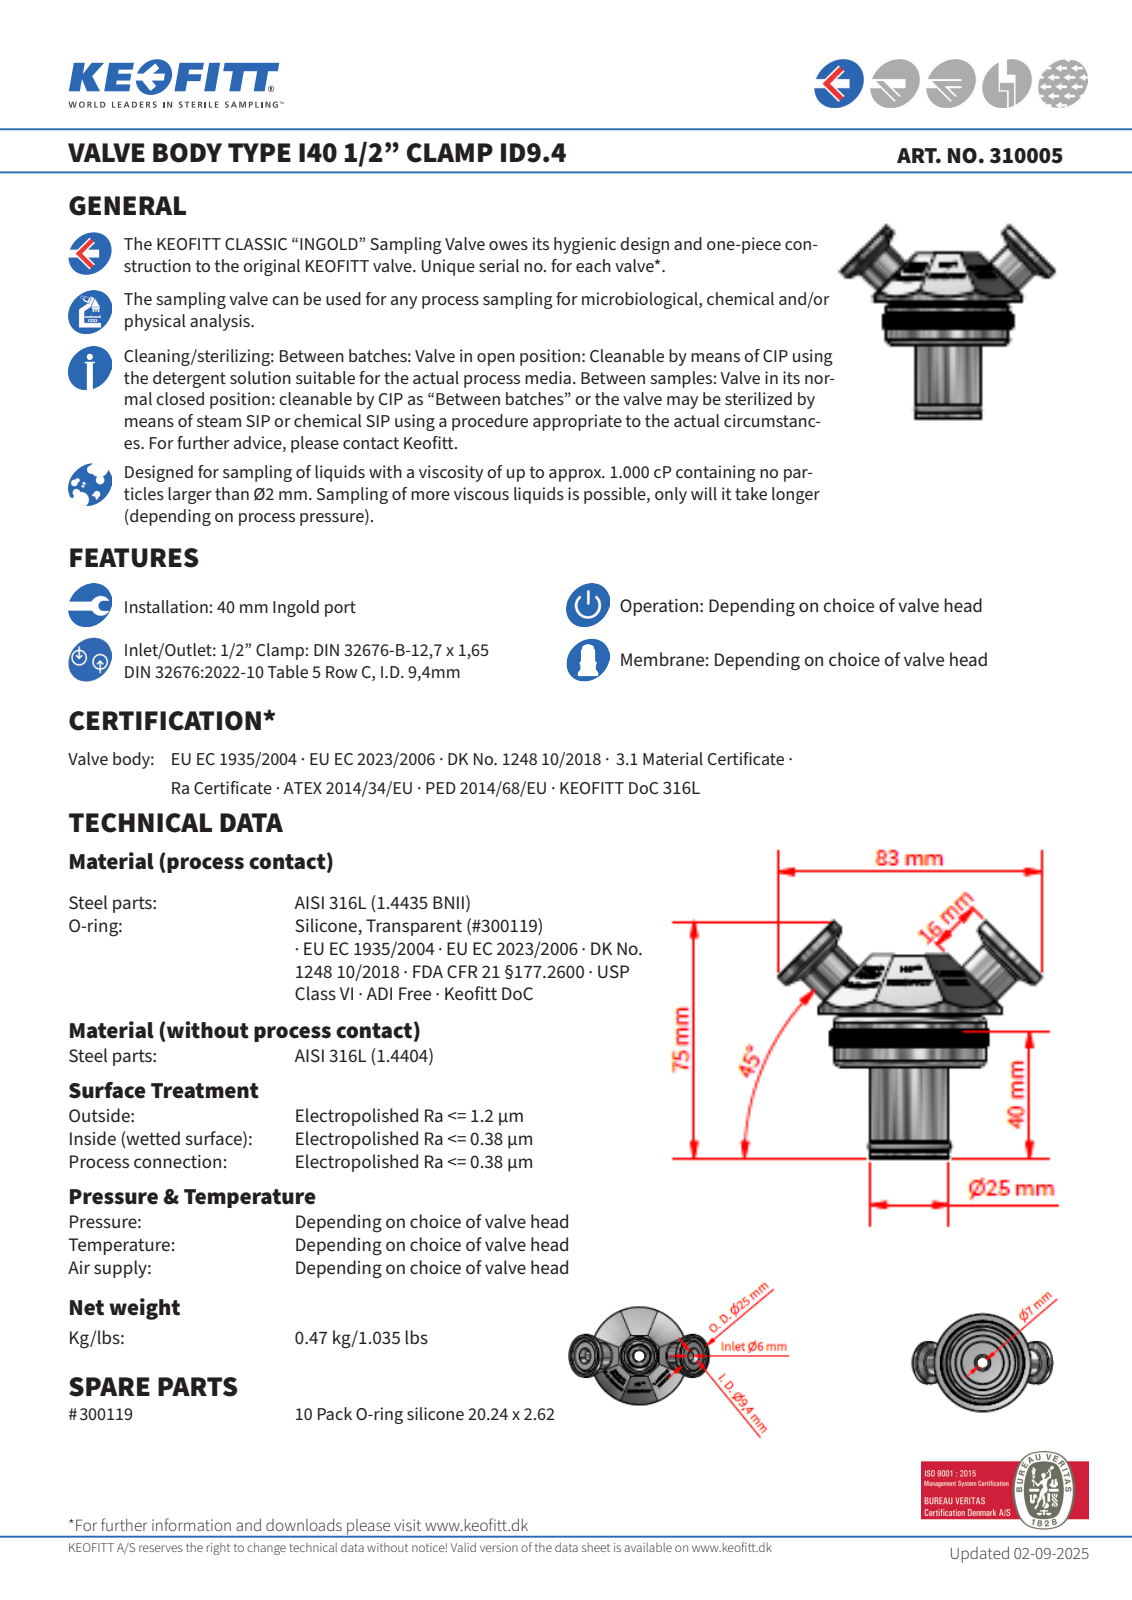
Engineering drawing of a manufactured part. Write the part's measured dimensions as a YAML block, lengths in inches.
part_name: "310005"
step_written_by: "Autodesk Inventor 2024 (AUTOMOTIVE_DESIGN)"
units: inches
bodies: {solids: 2, faces: 10681, planar: 17, cylindrical: 1632, other: 9032}
overall_size: [3.281, 2.954, 2.283]
volume: 5.051
surface_area: 26.2
round_bosses_or_shafts:
  - {diameter: 0.984, count: 3}
  - {diameter: 0.591, count: 2}
  - {diameter: 2.283, count: 1}
  - {diameter: 1.89, count: 1}
  - {diameter: 1.417, count: 1}
  - {diameter: 0.819, count: 1}
partial_cylinders:
  - {radius: 0.984, count: 1}
face_to_face_distances: [0.65, 0.63, 0.02, 1.398, 0.768, 0.748, 1.142, 1.772, 1.791, 2.539]
